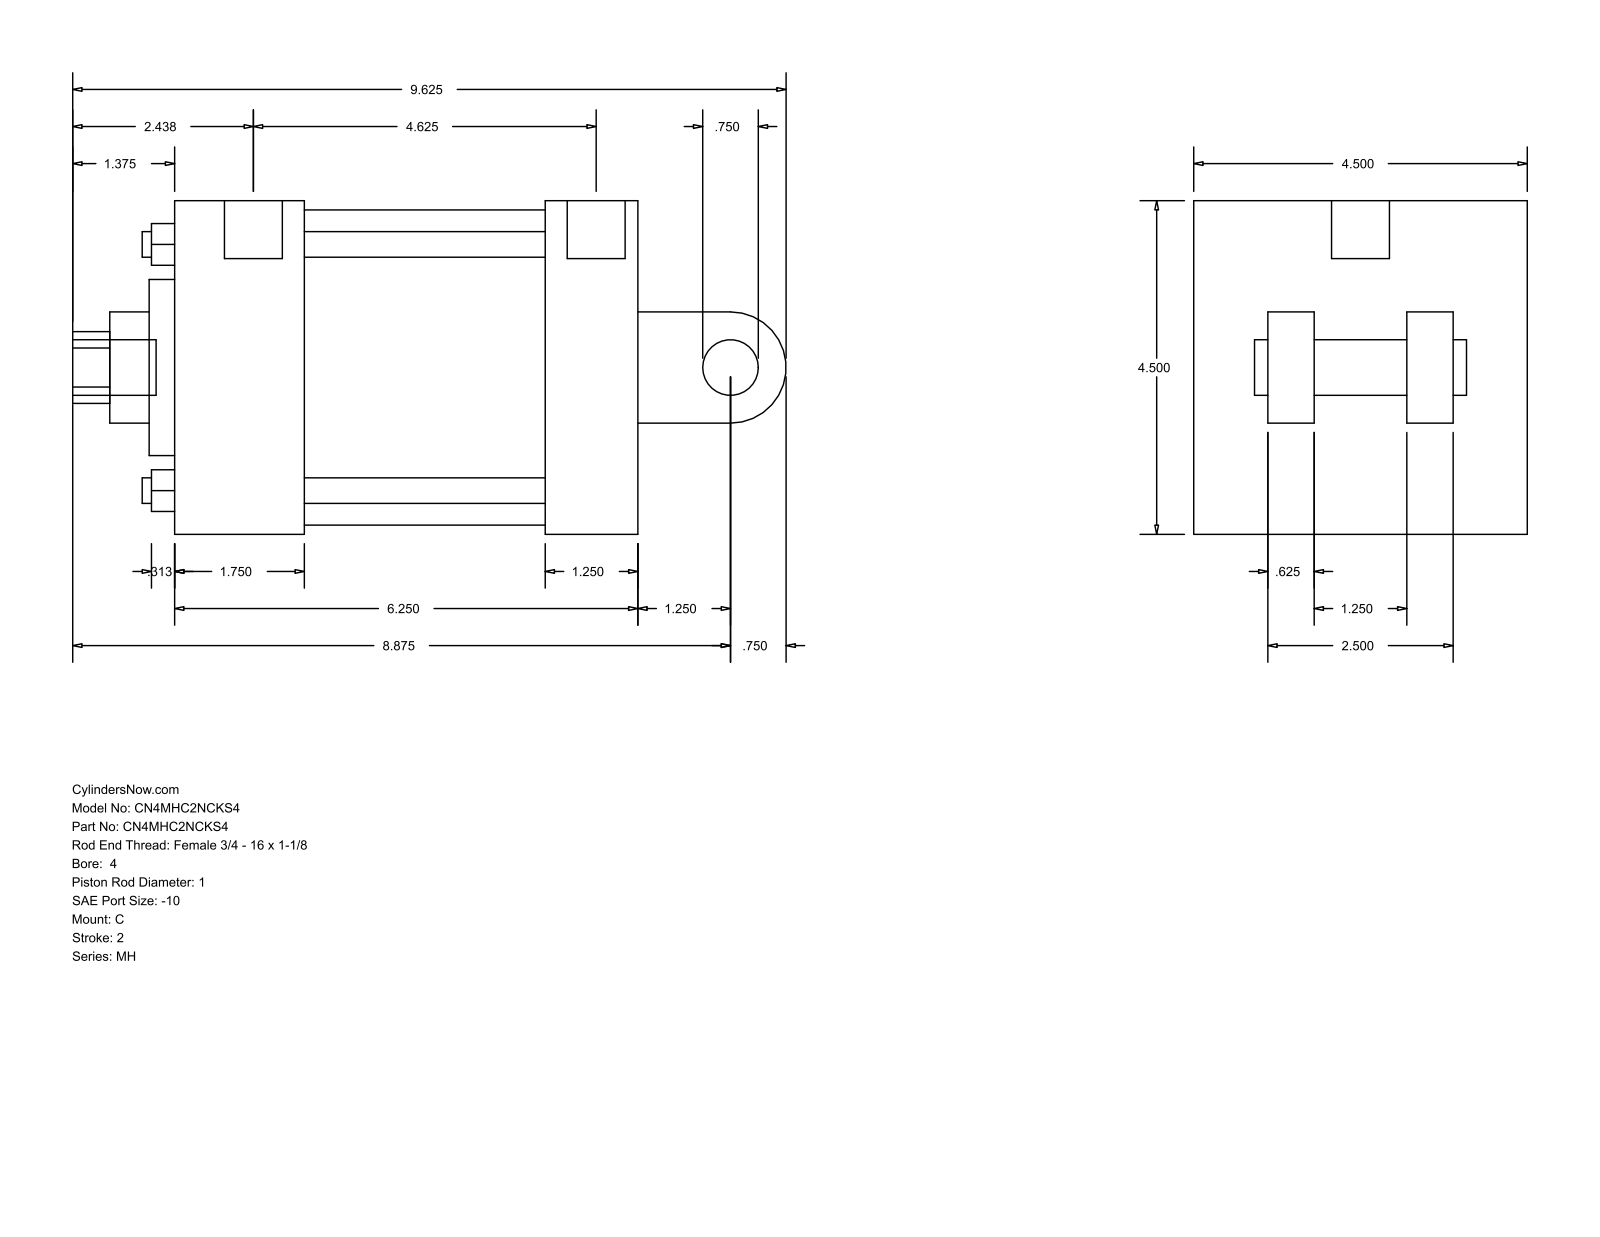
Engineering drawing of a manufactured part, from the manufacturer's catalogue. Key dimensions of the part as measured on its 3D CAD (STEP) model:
Part name (STEP PRODUCT): MH_C__0400_1
STEP written by: GSSL Pune (CONFIG_CONTROL_DESIGN)
Units: millimetres
Bodies: 0 solids, 101 faces (71 planar, 30 cylindrical, 0 other)
Overall size (bounding box): 244.47 × 114.3 × 114.3
Round holes (diameter × count): ⌀8.76 ×4, ⌀8.73 ×2, ⌀19.84 ×1, ⌀25.4 ×1, ⌀38.1 ×1, ⌀60.33 ×1, ⌀107.95 ×1
Round bosses / shafts (diameter × count): ⌀19.05 ×2, ⌀8.73 ×2, ⌀19.84 ×1
Partial cylindrical surfaces — rounded edges, fillets, slot ends (radius × count): R12.29 ×1, R19.05 ×1
Main face-to-face distances: 114.3, 158.76, 44.46, 127.01, 82.55, 31.75, 73.03, 15.87, 47.63, 38.1
Hole centre spacings: 59.62, 84.32, 119.25, 1.58
